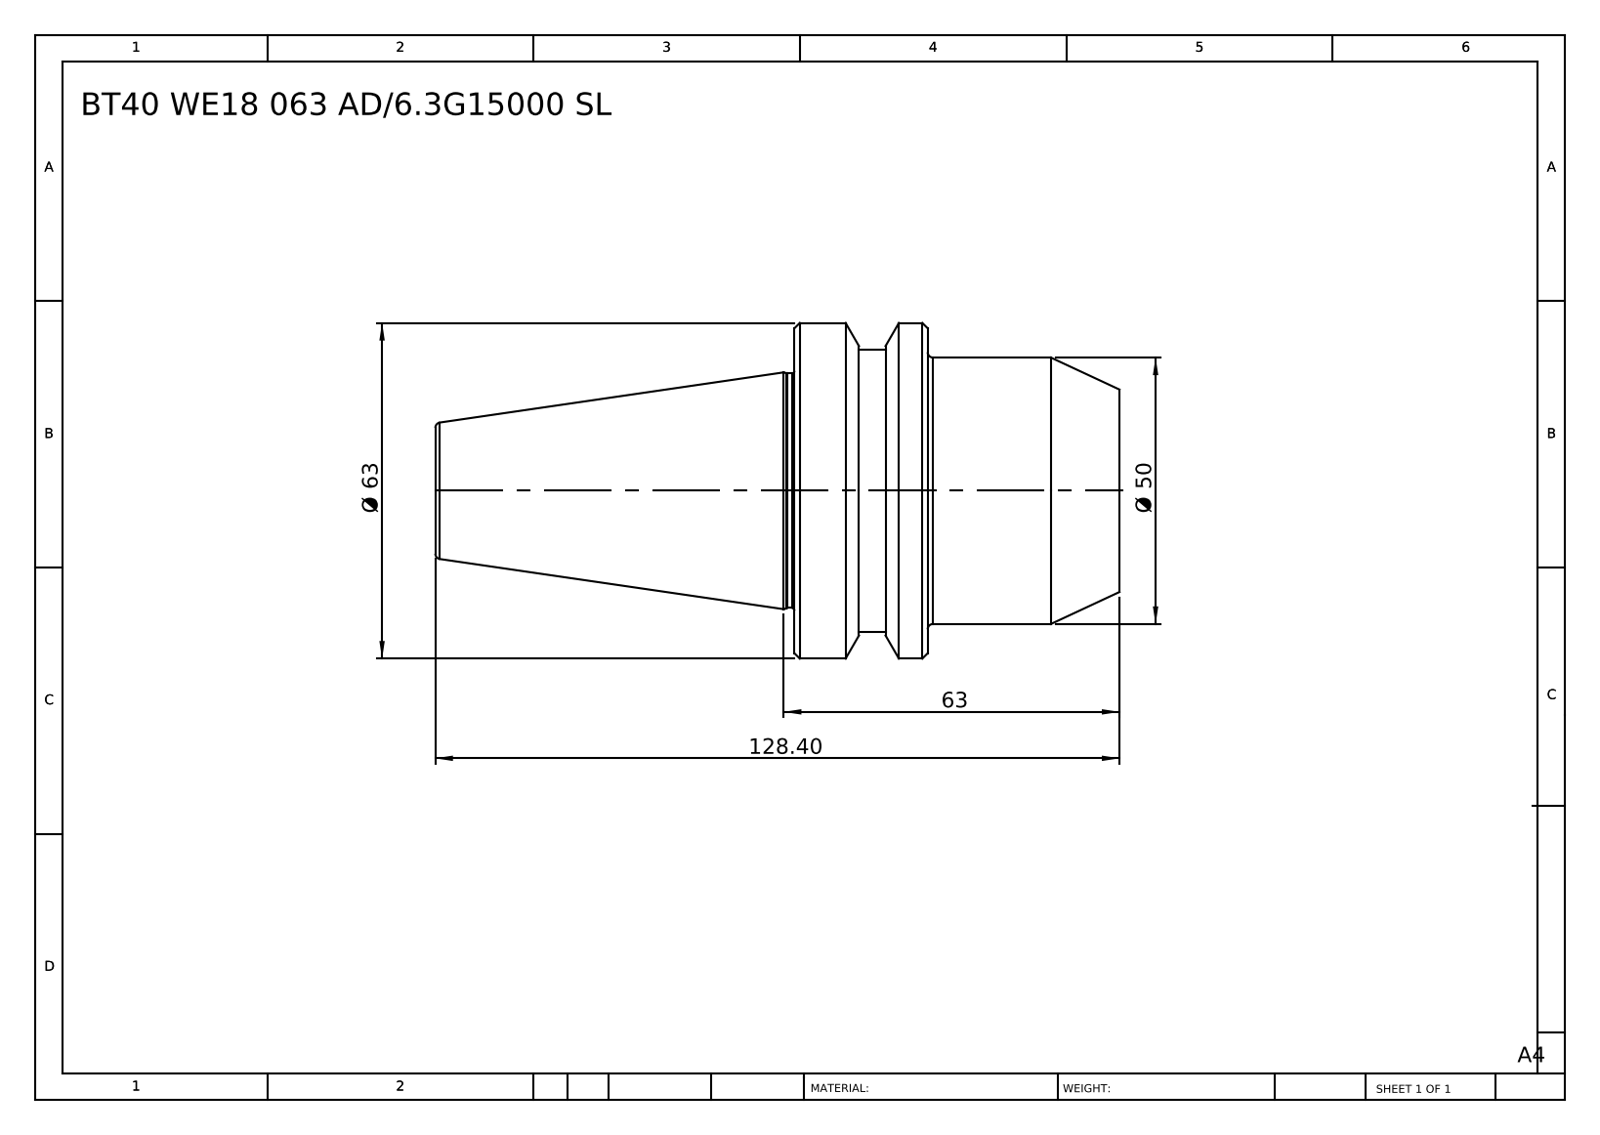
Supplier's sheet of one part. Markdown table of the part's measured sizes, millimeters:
| quantity | value |
| --- | --- |
| part name | BT40 WE18 063 AD-6.3G15000 SL |
| STEP written by | SolidWorks 2014 (CONFIG_CONTROL_DESIGN) |
| units | millimeters |
| bodies | 1 solid, 38 faces (6 planar, 10 cylindrical, 22 other) |
| overall size | 128.4 × 63 × 63 |
| volume | 203 488 mm³ |
| surface area | 23 032 mm² |
| round bosses / shafts (diameter × count) | 63 × 1, 53 × 1, 50 × 1, 44 × 1 |
| main face-to-face distances | 61, 36, 25, 128.4, 92.4, 67.4, 48.9, 12.9, 12.1, 79.5 |
